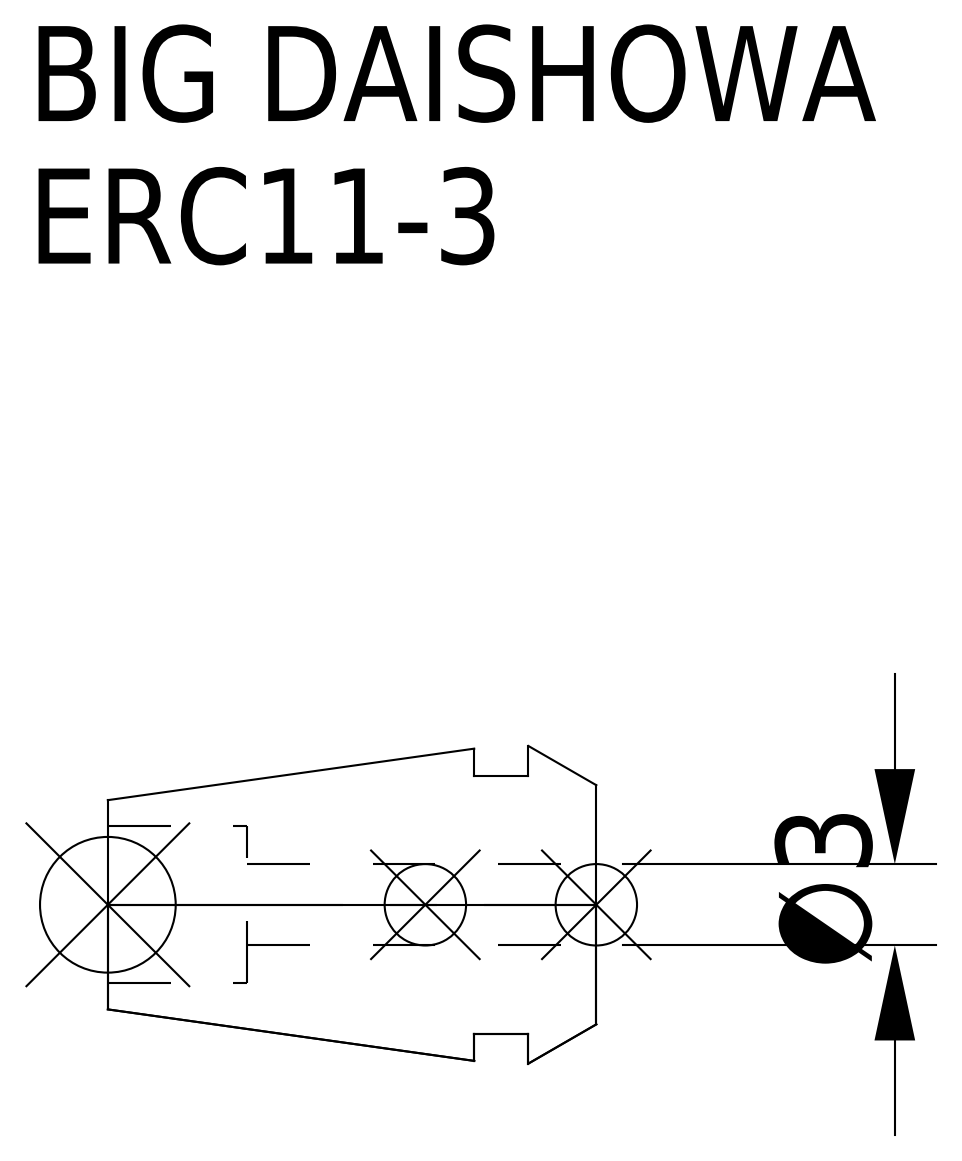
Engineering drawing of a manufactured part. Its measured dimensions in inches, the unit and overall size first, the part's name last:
Units: inches
Overall size (bounding box): 0.709 × 0.461 × 0.461
Round holes (diameter × count): ⌀0.118 ×1, ⌀0.228 ×1
Round bosses / shafts (diameter × count): ⌀0.374 ×1
Main face-to-face distances: 0.098, 0.177, 0.079, 0.709, 0.61, 0.531, 0.507, 0.408, 0.33, 0.202
Volume: 0.068 in³ · Surface area: 1.46 in²
Bodies: 1 solid, 15 faces (5 planar, 6 cylindrical, 4 other)
Part name (STEP PRODUCT): ERC11-3
STEP written by: CREO PARAMETRIC BY PTC INC, 2016380 (AUTOMOTIVE_DESIGN)
